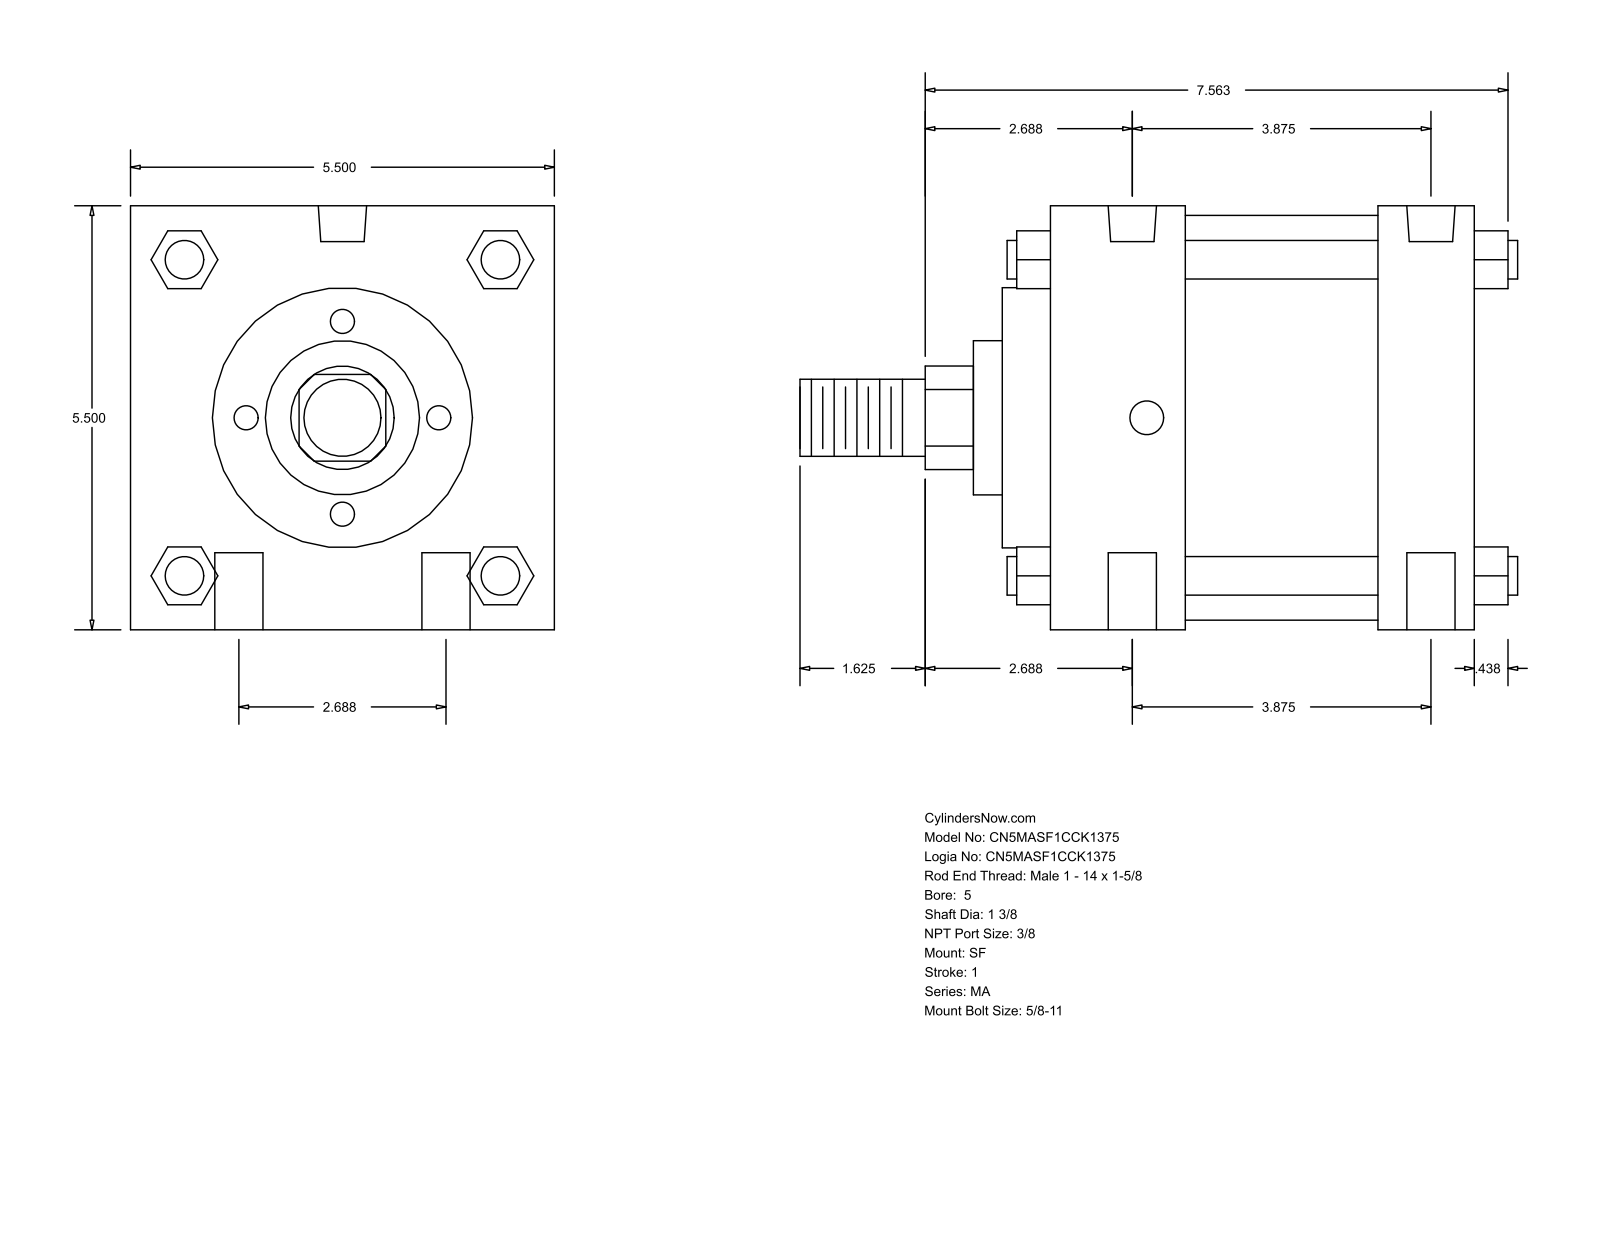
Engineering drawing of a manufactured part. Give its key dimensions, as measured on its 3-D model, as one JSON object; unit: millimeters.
{"part_name": "MA_SF__0500_1.375", "step_written_by": "GSSL Pune (CONFIG_CONTROL_DESIGN)", "units": "millimeters", "bodies": {"solids": 0, "faces": 126, "planar": 95, "cylindrical": 31, "other": 0}, "overall_size": [236.54, 139.7, 139.7], "round_holes": [[15.88, 4], [11.11, 2], [15.93, 2]], "round_bosses_or_shafts": [[12.7, 4], [133.35, 1], [85.72, 1], [50.8, 1], [34.92, 1], [25.4, 1]], "partial_cylinders_radius": [[17.06, 1]], "face_to_face_distances": [139.7, 44.45, 107.95, 63.5, 95.25, 31.75, 15.87, 60.32, 123.82, 155.57], "hole_center_spacings": [34.13, 104.18, 98.43, 68.26, 119.78, 88.9]}
